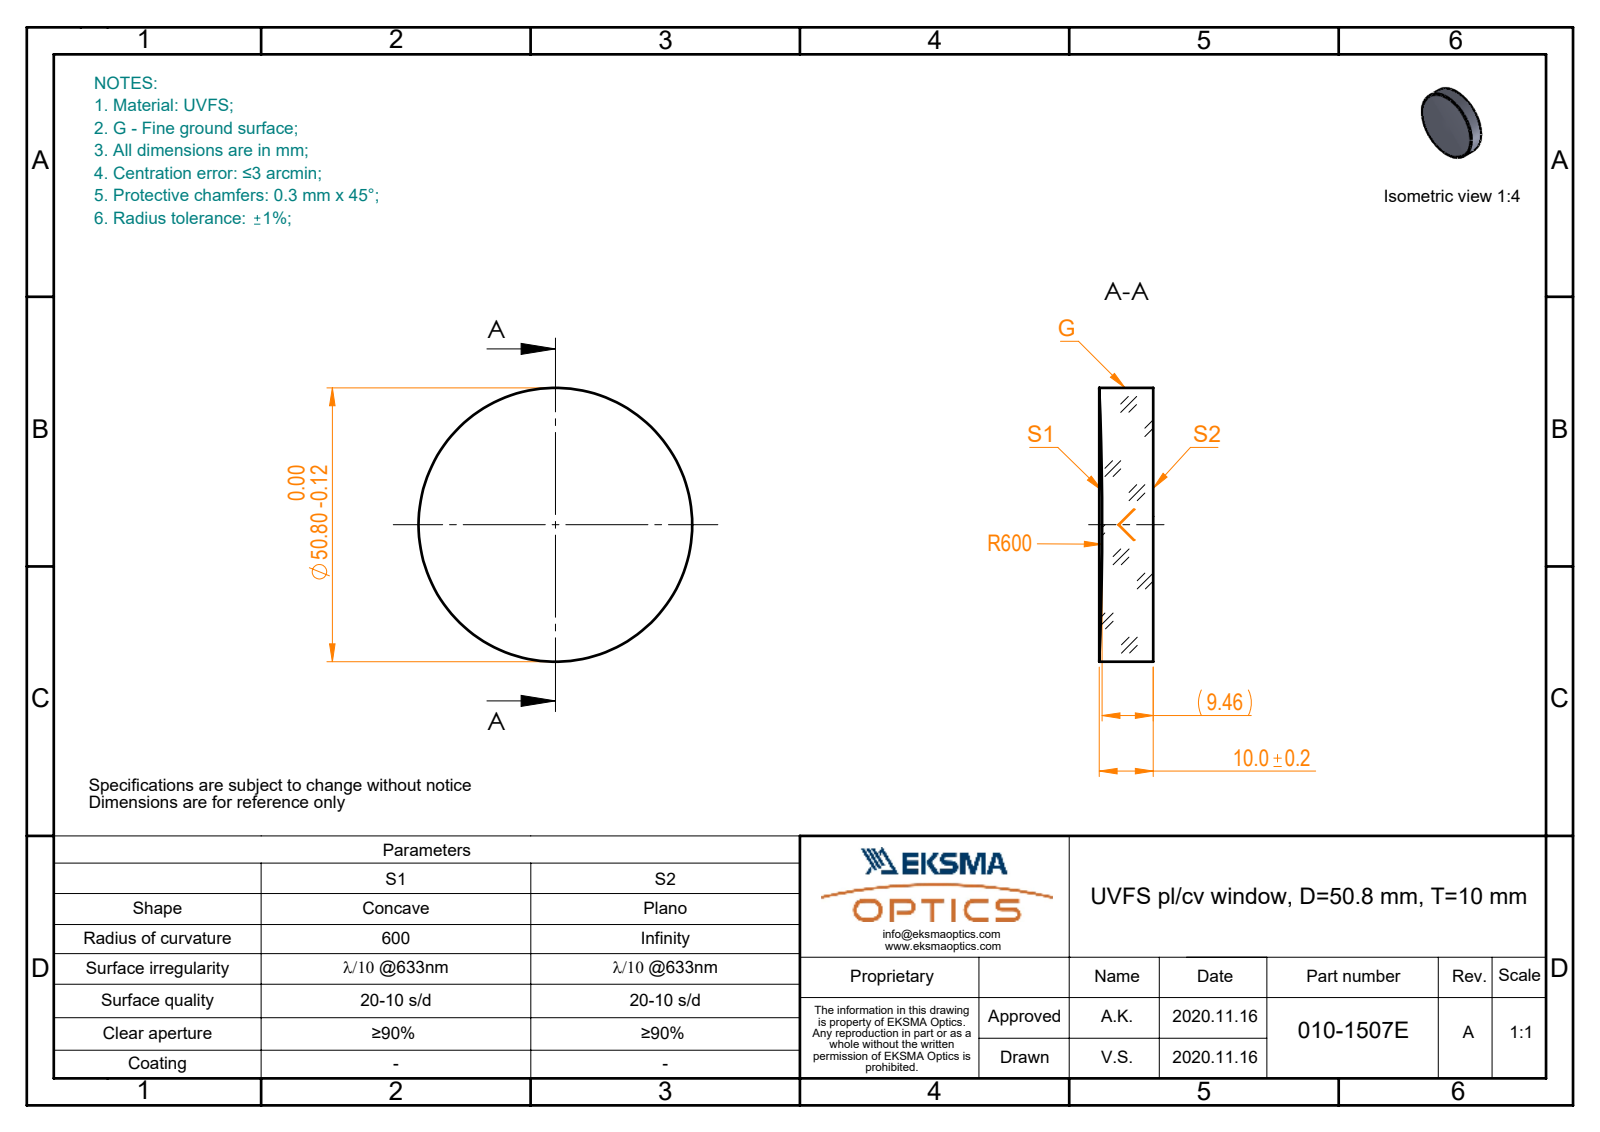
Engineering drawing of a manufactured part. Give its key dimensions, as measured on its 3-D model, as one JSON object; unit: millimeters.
{"part_name": "010-1507E_UVFS_PCV_window", "step_written_by": "SolidWorks 2019 (CONFIG_CONTROL_DESIGN)", "units": "millimeters", "bodies": {"solids": 1, "faces": 5, "planar": 1, "cylindrical": 2, "other": 2}, "overall_size": [50.8, 50.8, 10], "volume_mm3": 19723, "surface_area_mm2": 5650, "round_bosses_or_shafts": [[50.8, 1]]}
